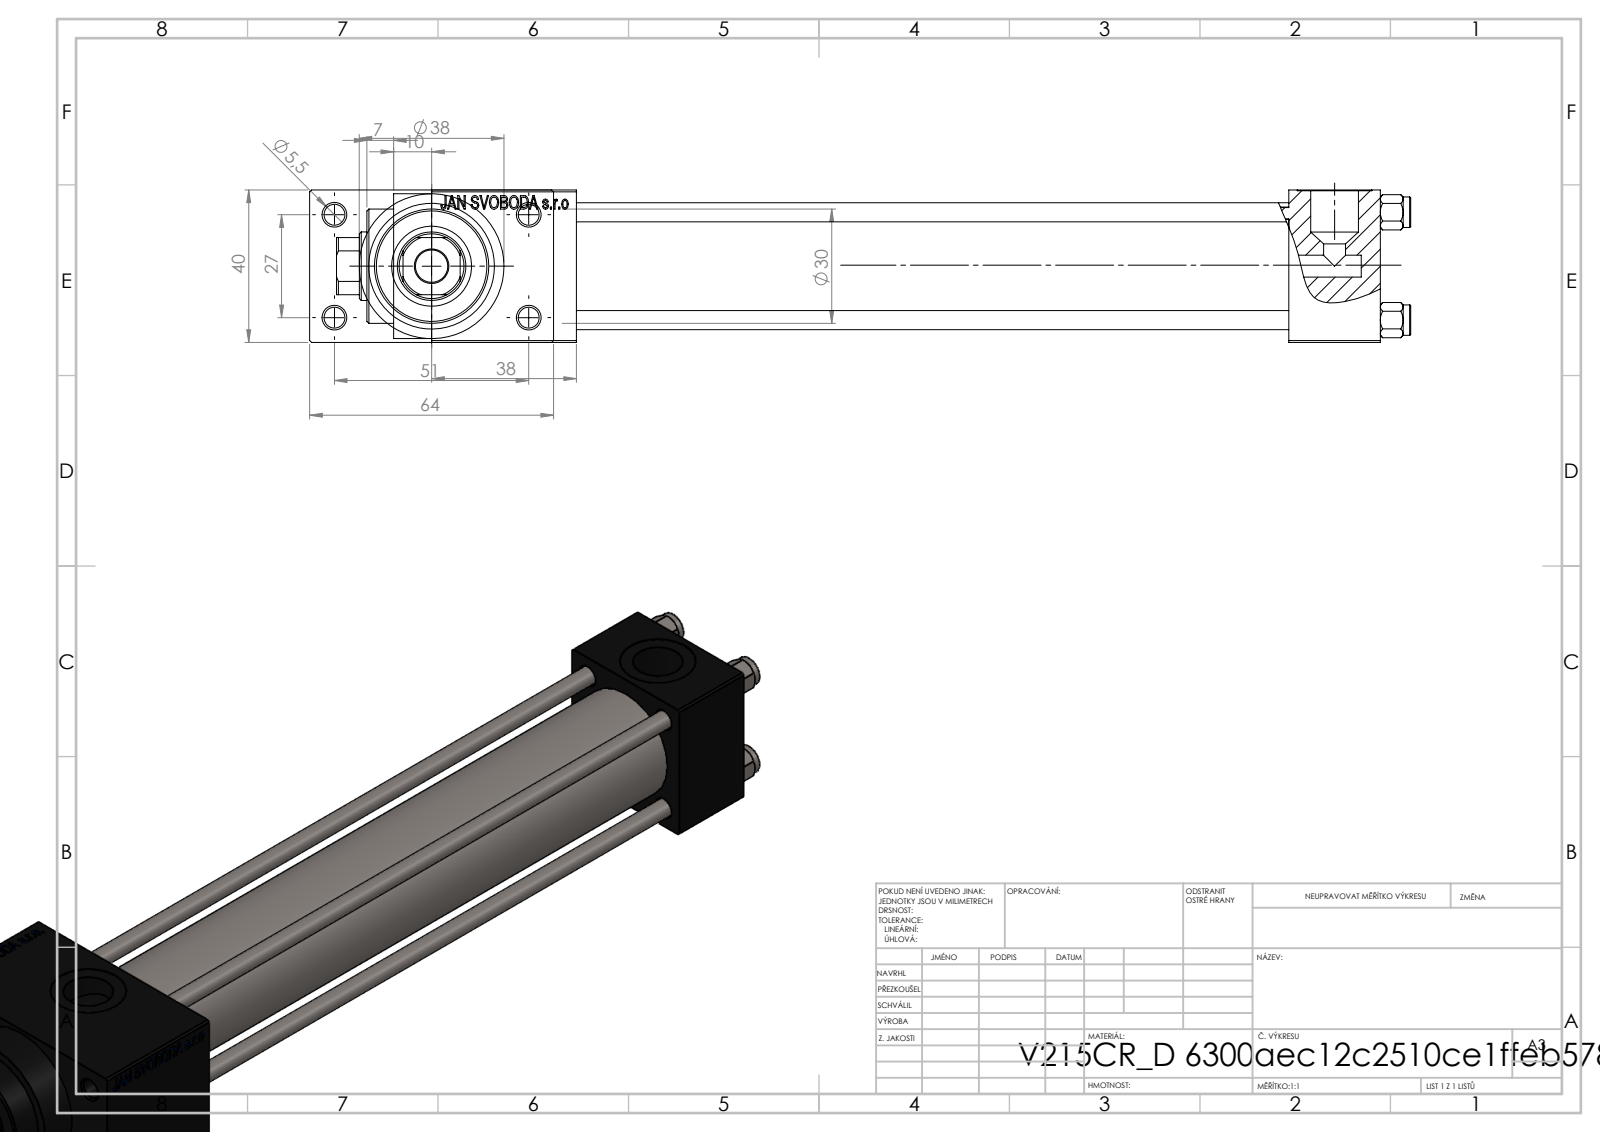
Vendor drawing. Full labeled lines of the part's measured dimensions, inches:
Part name (STEP PRODUCT): V215CR_D_Body; NUT_M5_D; V215_VC_A; V215CR_VCP_D (+1 more)
STEP written by: SolidWorks 2019 (CONFIG_CONTROL_DESIGN)
Units: inches
Bodies: 11 solids, 1102 faces (495 planar, 87 cylindrical, 520 other)
Overall size (bounding box): 11.102 × 2.52 × 1.575
Volume: 16.12 in³ · Surface area: 163.5 in²
Round holes (diameter × count): ⌀0.197 ×4, ⌀0.217 ×4, ⌀0.787 ×3, ⌀0.276 ×2, ⌀0.518 ×2, ⌀0.335 ×1, ⌀0.709 ×1, ⌀0.827 ×1, ⌀0.984 ×1, ⌀1.181 ×1
Round bosses / shafts (diameter × count): ⌀0.315 ×4, ⌀1.496 ×1, ⌀1.22 ×1
Partial cylindrical surfaces — rounded edges, fillets, slot ends (radius × count): R0.335 ×1
Main face-to-face distances: 1.575, 0.472, 2.047, 7.362, 0.945, 8.307, 2.52, 1.496, 9.803, 8.858
Hole centre spacings: 0.448, 0.788, 1.114, 1.136, 1.177, 1.561, 1.903, 1.063
